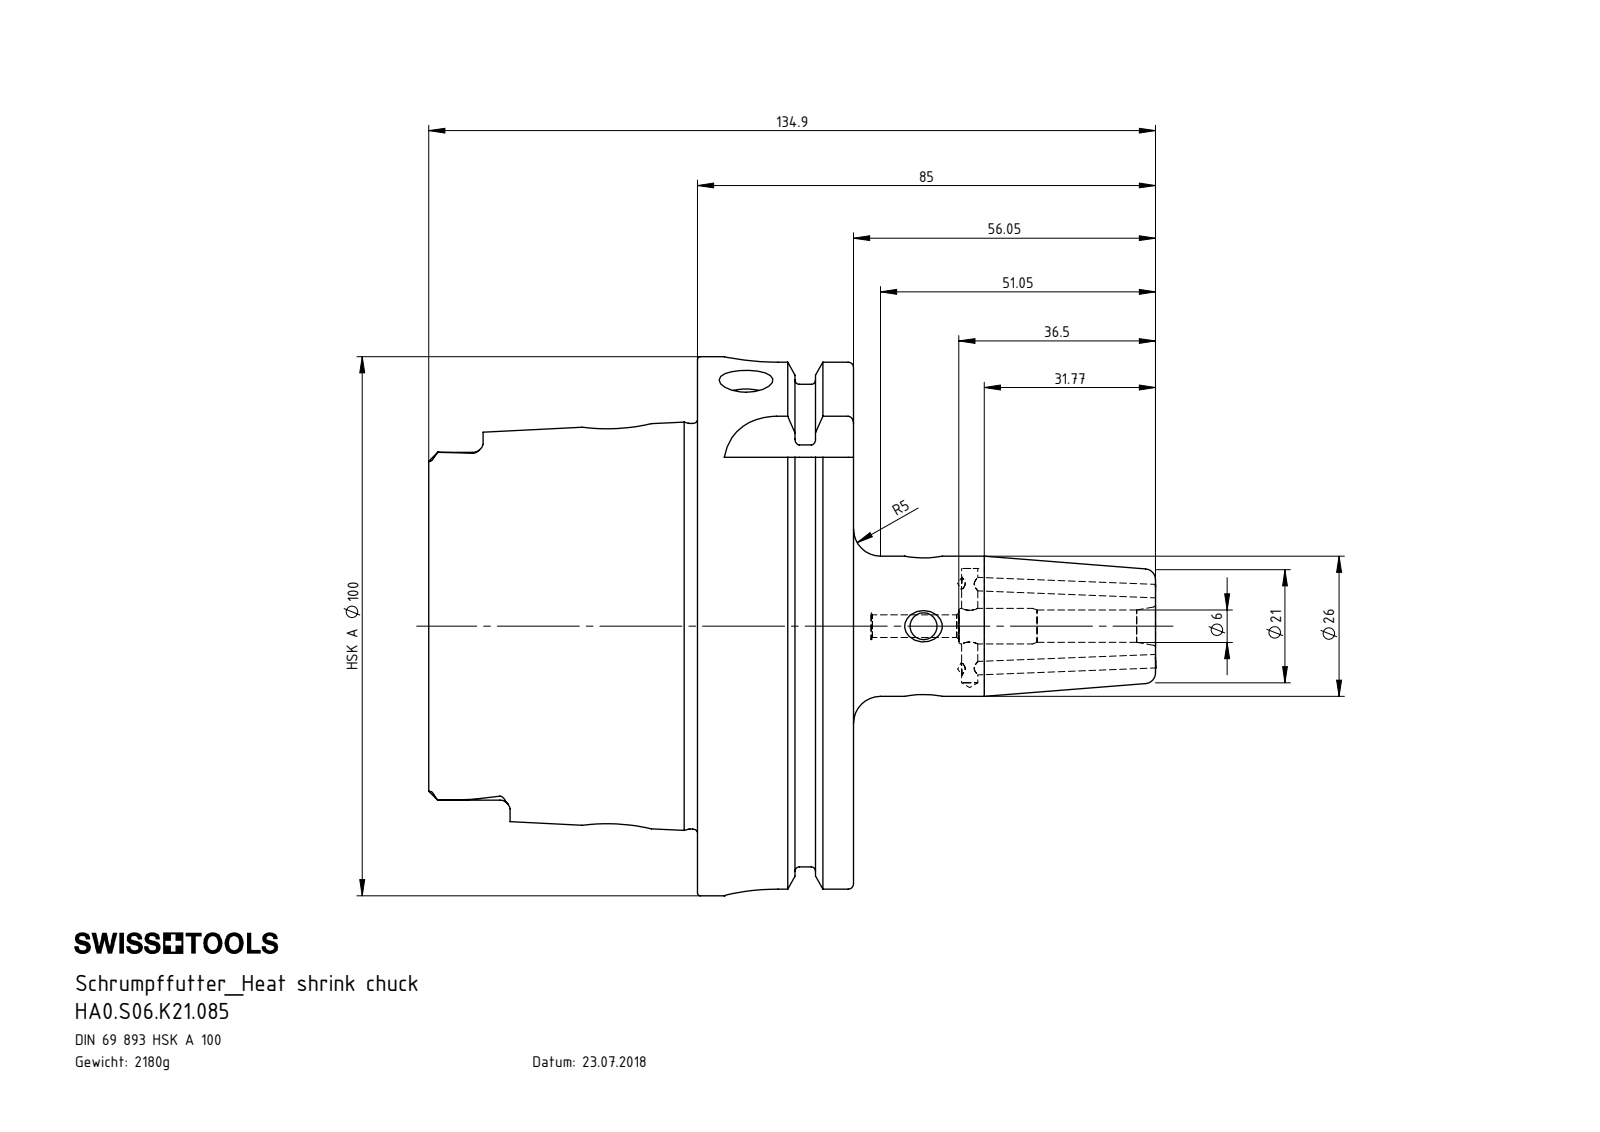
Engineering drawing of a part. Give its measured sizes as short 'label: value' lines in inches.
name: HA0-S06.K21.085_C_Fertigbearbeitung; ERU-AN1.K01.014_A; ERU-CJ2.001.006; HA0.S06.K21.085
written by: SolidWorks 2017 (CONFIG_CONTROL_DESIGN)
unit: in
bodies: 4 solids, 299 faces (95 planar, 86 cylindrical, 118 other)
size: 5.314 × 3.937 × 3.937
volume: 16.95 in³; area: 87.42 in²
holes: 3× ⌀0.098, 3× ⌀0.197, 3× ⌀0.394, 1× ⌀0.118, 1× ⌀0.165, 1× ⌀0.236, 1× ⌀0.26, 1× ⌀0.472, 1× ⌀0.886, 1× ⌀1.024, 1× ⌀2.087, 1× ⌀2.48
bosses: 2× ⌀0.118, 1× ⌀3.937, 1× ⌀3.62, 1× ⌀2.963
rounds: 6× R0.075, 4× R0.192, 4× R0.394
face distances: 1.14, 0.49, 0.65, 1.965, 2.455, 3.104, 3.079, 1.114, 0.624, 0.026
hole spacings: 0.337, 1.376, 2.242, 2.579
